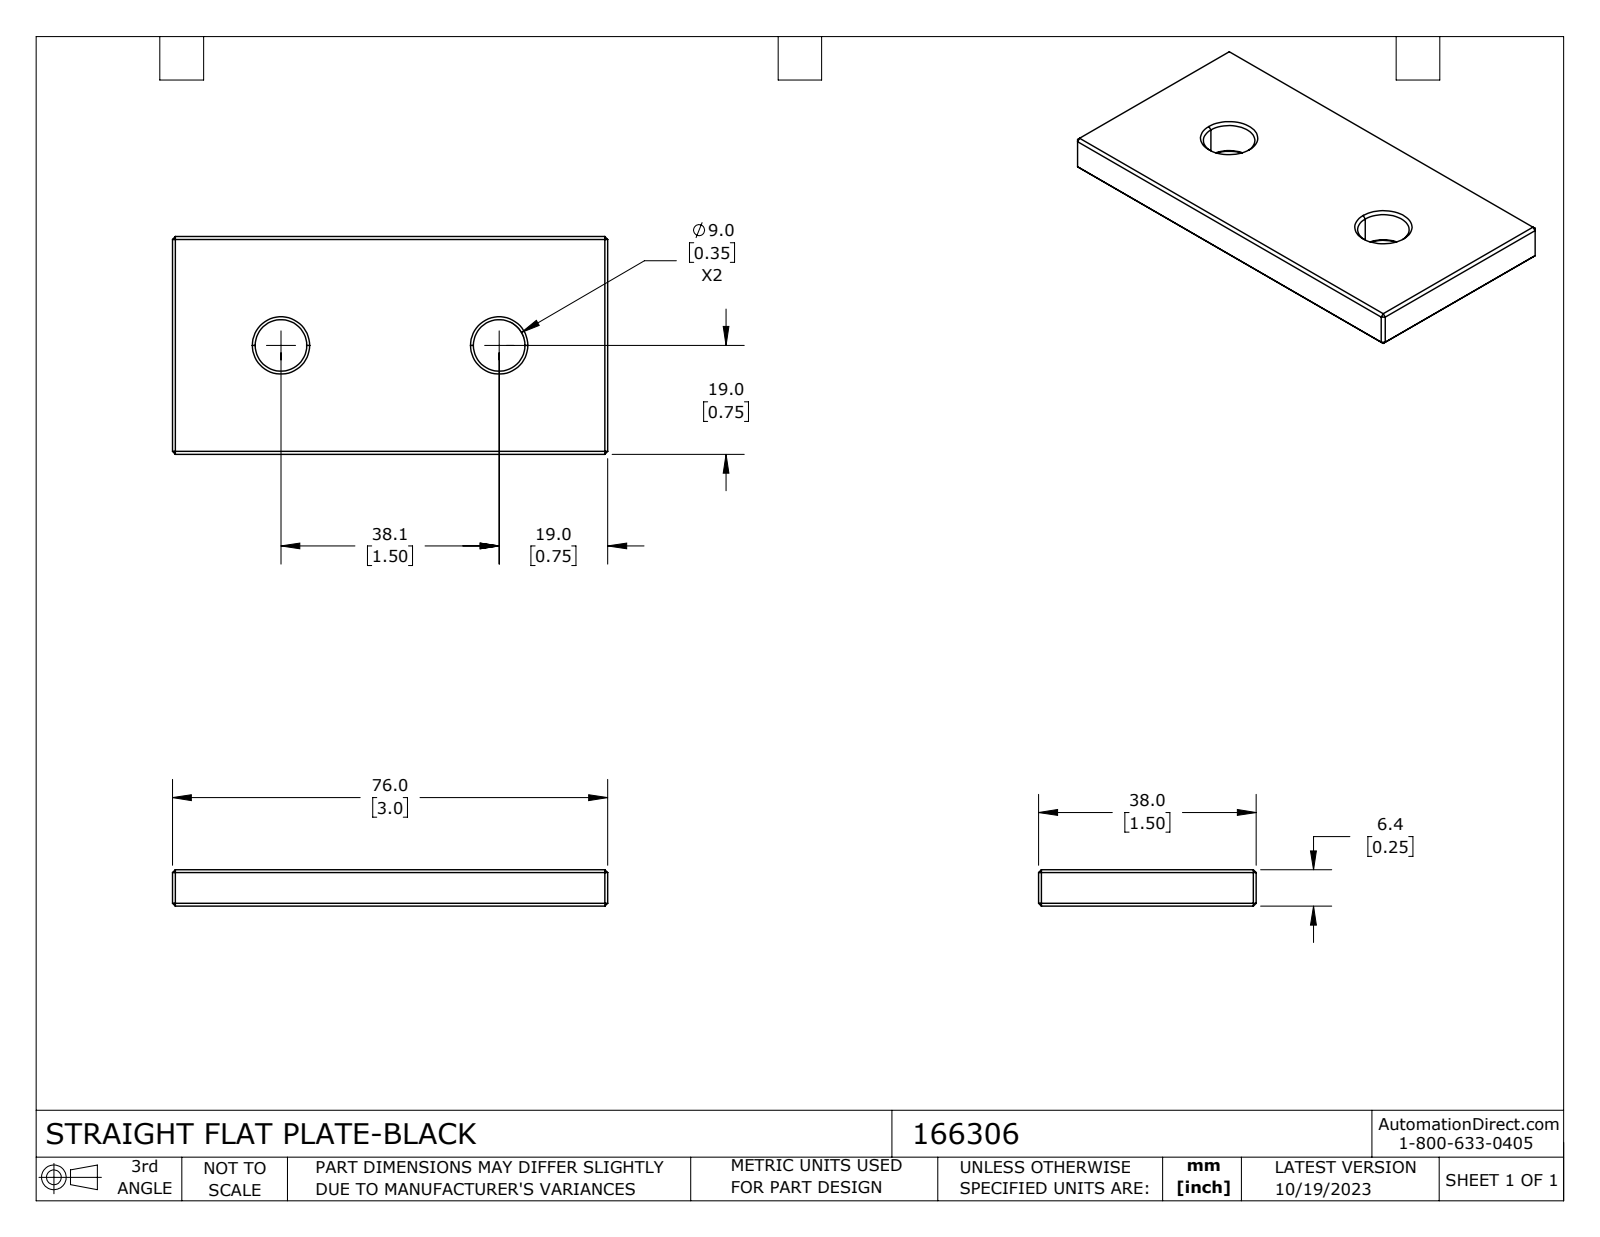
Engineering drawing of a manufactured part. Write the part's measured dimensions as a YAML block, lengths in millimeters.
part_name: "166306"
step_written_by: "SolidWorks 2023 (CONFIG_CONTROL_DESIGN)"
units: millimeters
bodies: {solids: 1, faces: 38, planar: 26, cylindrical: 4, other: 8}
overall_size: [76, 38, 6.35]
volume: 17457
surface_area: 7155
round_holes:
  - {diameter: 9, count: 2}
face_to_face_distances: [6.35, 38, 76, 30.65, 57.51, 79.9, 68.29]
hole_center_spacings: [38.1]
